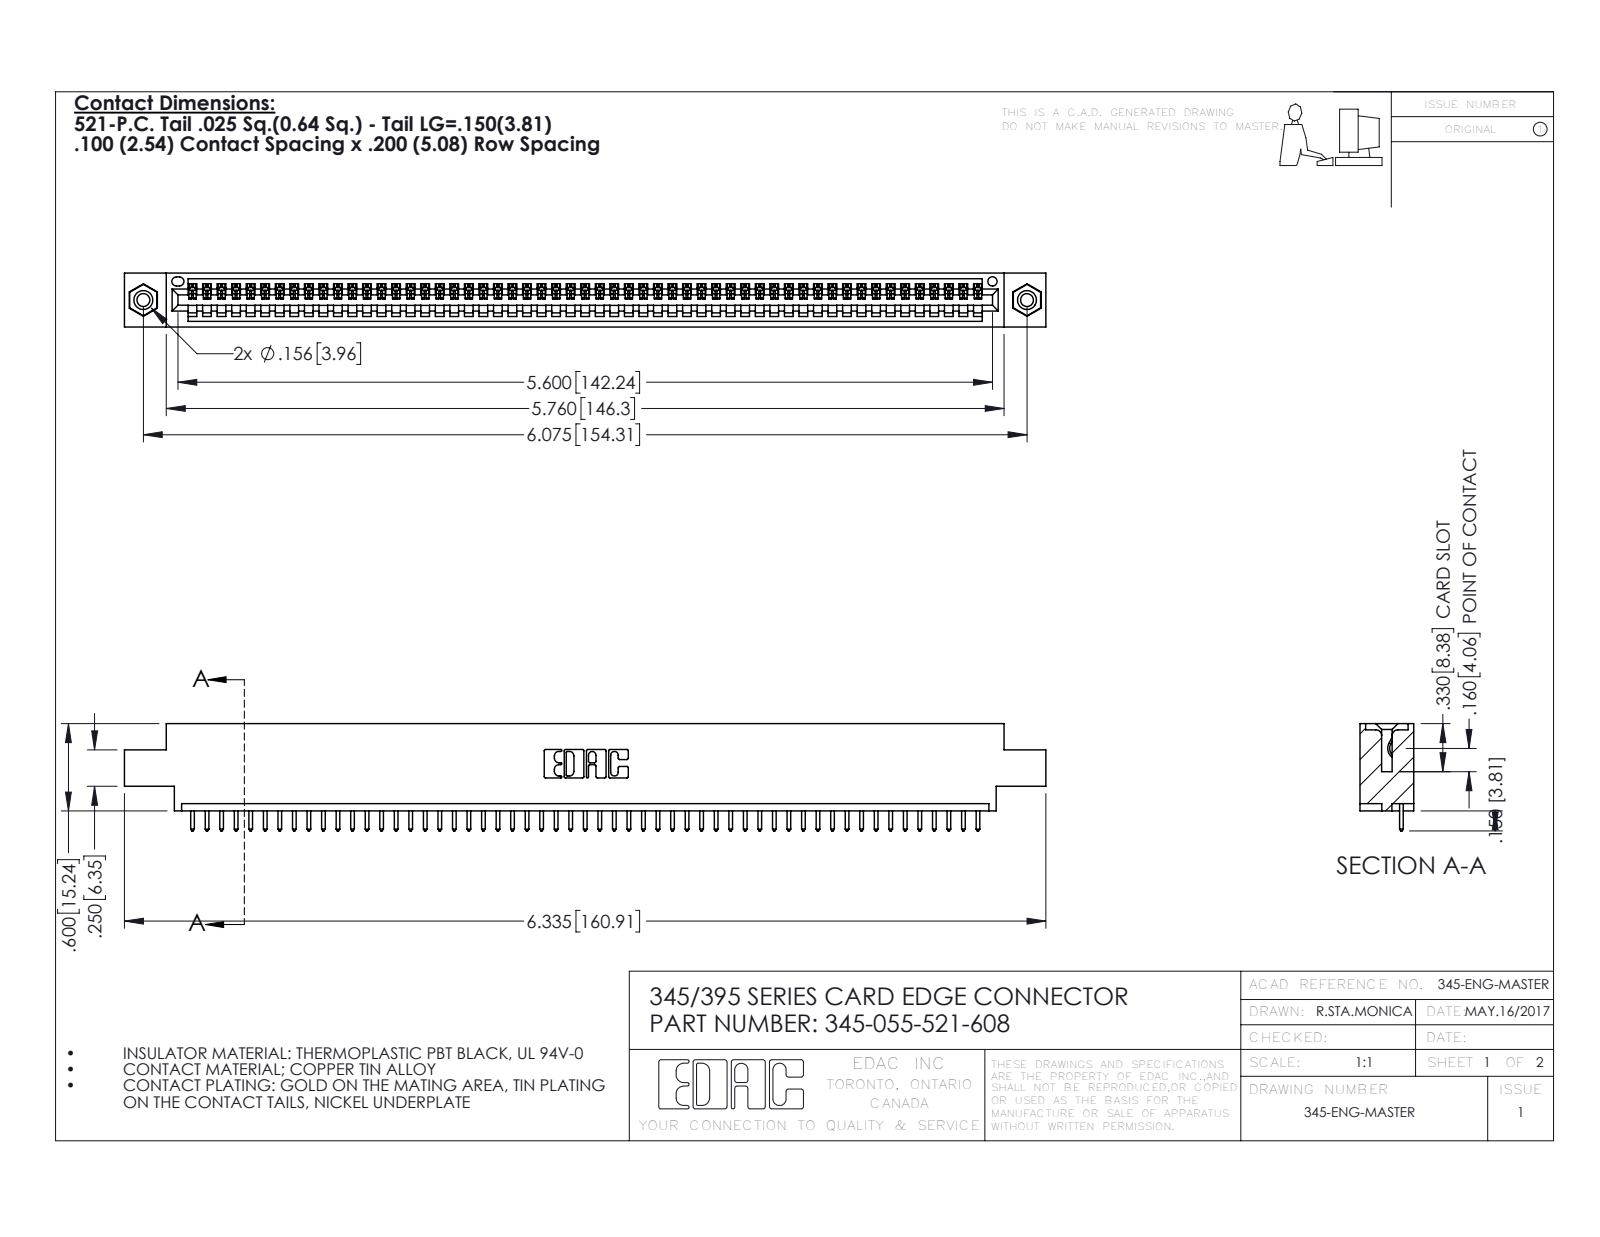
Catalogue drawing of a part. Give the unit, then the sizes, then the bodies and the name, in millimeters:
Units: millimetres
Overall size (bounding box): 160.9 × 18.7 × 9.4
Round holes (diameter × count): ⌀2.3 ×2, ⌀3.2 ×2, ⌀4 ×2, ⌀1.6 ×1
Round bosses / shafts (diameter × count): ⌀3.9 ×2
Partial cylindrical surfaces — rounded edges, fillets, slot ends (radius × count): R0.2 ×110, R0.3 ×110, R0.3 ×22, R0.2 ×6, R0.8 ×6, R0.7 ×3, R0.8 ×2, R1 ×2
Main face-to-face distances: 1.8, 7.6, 9.4, 5.1, 2.5, 6.9, 0.6, 5.7, 4.4, 3.8
Hole centre spacings: 6.9, 148.3, 154.3
Volume: 15 100 mm³ · Surface area: 19 790 mm²
Bodies: 58 solids, 3380 faces (2316 planar, 1048 cylindrical, 16 other)
Part name (STEP PRODUCT): 345-250-001_345-250-003-102; 345-055-521-608; 345 Part_0.170 Offset - 0.156 Dia-TI; 345-292-001_345-293-121
STEP written by: SolidWorks 2016 (CONFIG_CONTROL_DESIGN)
